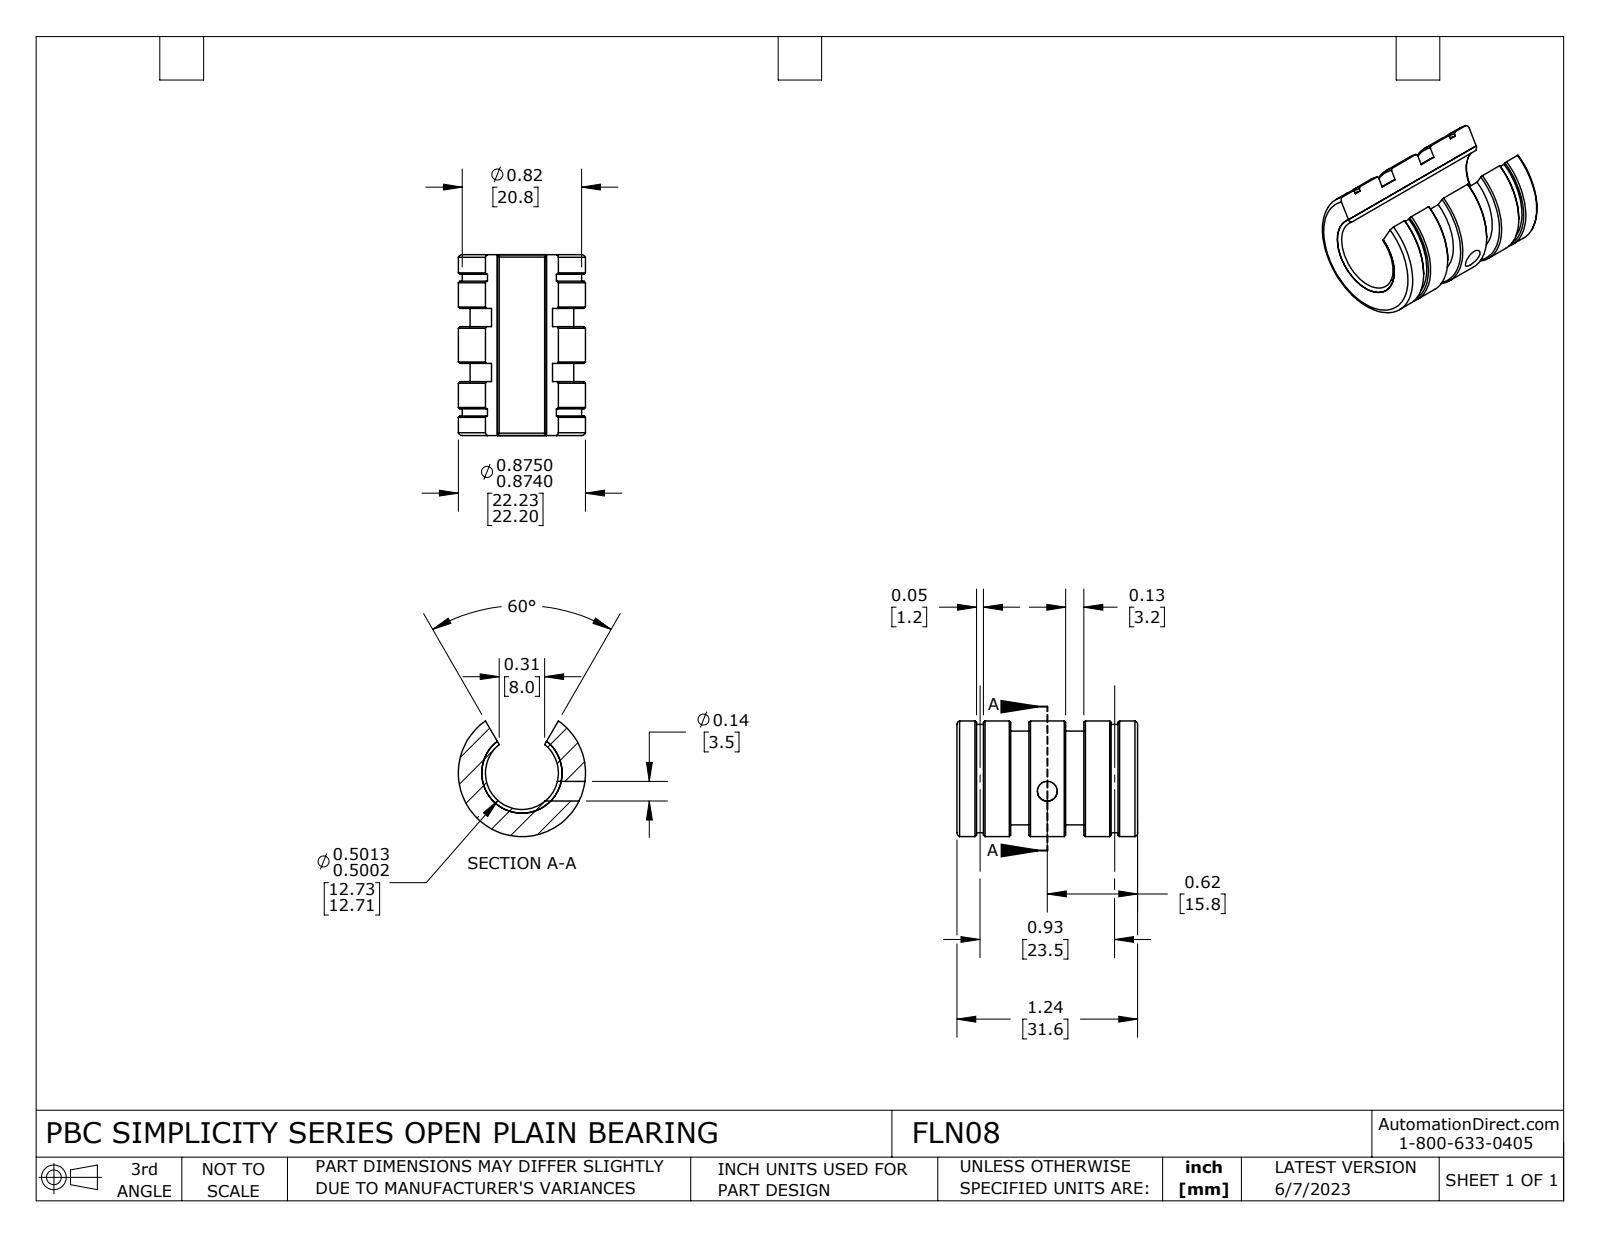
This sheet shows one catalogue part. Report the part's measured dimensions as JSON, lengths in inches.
{"part_name": "FLN08", "step_written_by": "SolidWorks 2021 (CONFIG_CONTROL_DESIGN)", "units": "inches", "bodies": {"solids": 2, "faces": 82, "planar": 14, "cylindrical": 40, "other": 28}, "overall_size": [1.243, 0.874, 0.795], "volume_in3": 0.349, "surface_area_in2": 9.352, "round_holes": [[0.136, 1]], "round_bosses_or_shafts": [[0.874, 1], [0.82, 1], [0.712, 1]], "partial_cylinders_radius": [[0.25, 1], [0.276, 1]], "face_to_face_distances": [0.495, 0.748, 0.37, 0.873, 0.125, 0.378, 1.243, 0.253, 0.503, 0.135]}
